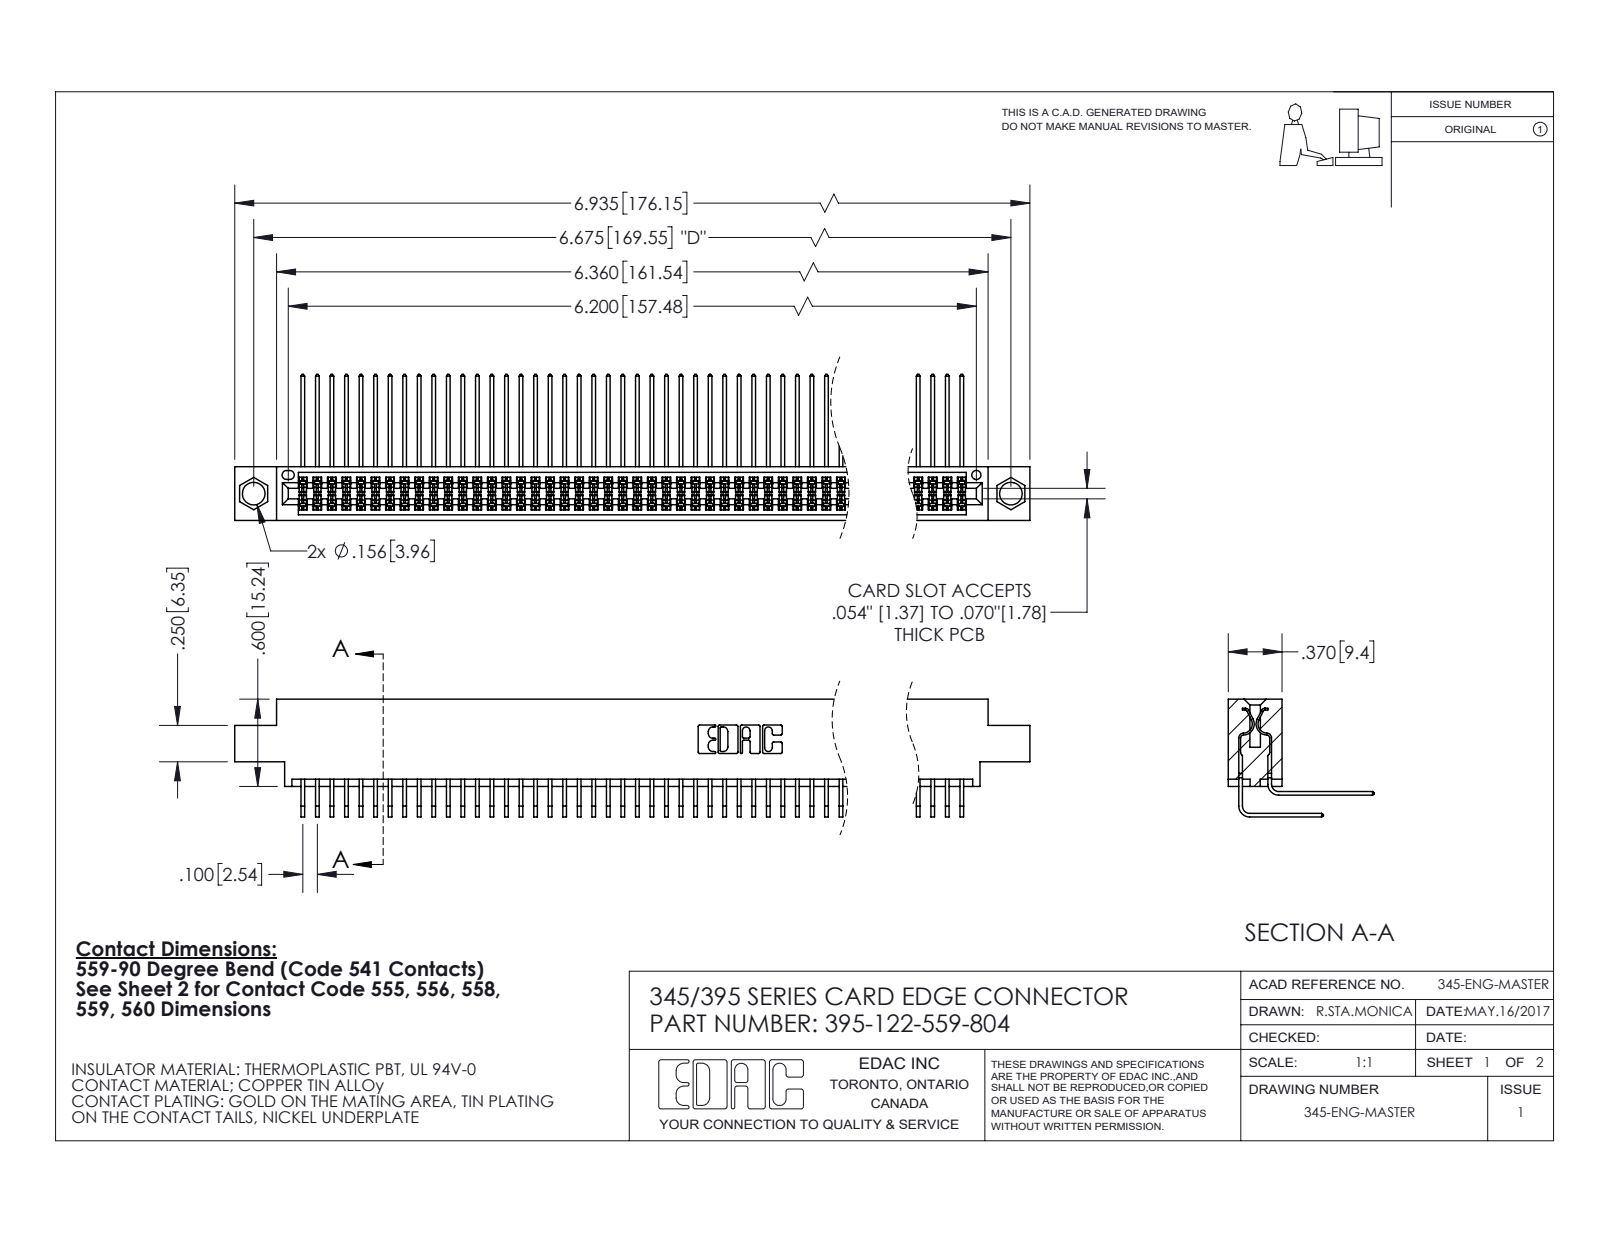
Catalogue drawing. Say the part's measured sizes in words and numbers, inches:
The part is named "345-292-001_558 559 Tail - 1; 345-292-001_559 Tail - 2; 395-122-559-804; 345 Part_0.170 Offset - 0.156 Dia-TI". Its 3-D file was written by "SolidWorks 2020 (CONFIG_CONTROL_DESIGN)". It is 123 solids with 6488 faces: 4368 planar, 2120 cylindrical and 0 other. Overall it measures 6.935 by 1.005 by 0.809 inches. Its volume is 1.085 cubic inches and its surface area 46.41 square inches. Round holes: 2 of diameter 0.156, 1 of diameter 0.064. Partial cylindrical surfaces (rounded edges, fillets, slot ends): 183 of radius 0.006, 22 of radius 0.01, 6 of radius 0.007, 6 of radius 0.031, 3 of radius 0.026, 2 of radius 0.014, 2 of radius 0.019, 2 of radius 0.022. The main face-to-face distances are 0.072, 0.298, 0.37, 0.2, 0.098, 0.272, 0.025, 0.225, 0.175, 0.15. The hole center spacings are 0.27, 6.439, 6.675.
